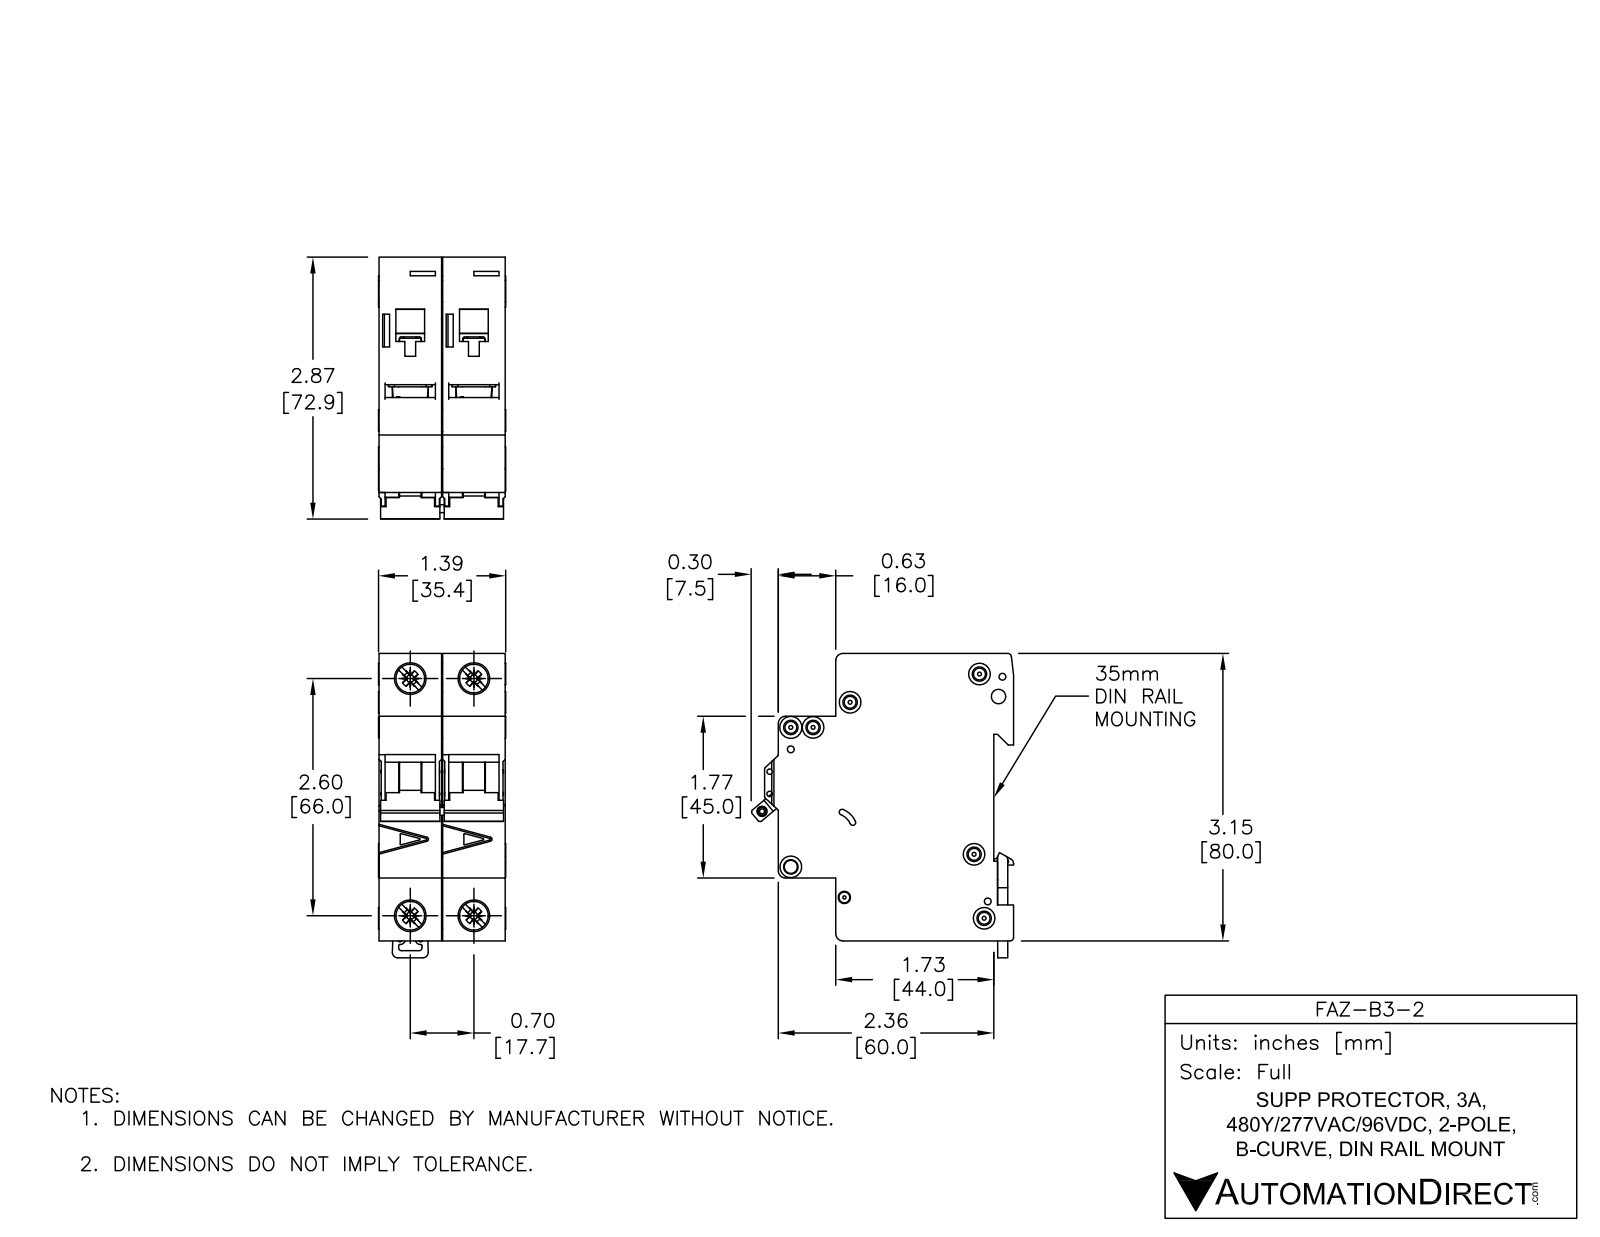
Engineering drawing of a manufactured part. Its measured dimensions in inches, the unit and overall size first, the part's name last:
Units: inches
Overall size (bounding box): 3.338 × 2.876 × 1.394
Round holes (diameter × count): ⌀0.142 ×6, ⌀0.075 ×3, ⌀0.043 ×2, ⌀0.059 ×2, ⌀0.157 ×2, ⌀0.281 ×2, ⌀0.323 ×2, ⌀0.085 ×1, ⌀0.087 ×1, ⌀0.1 ×1, ⌀0.13 ×1, ⌀0.134 ×1
Round bosses / shafts (diameter × count): ⌀0.236 ×4, ⌀0.323 ×2, ⌀0.098 ×2
Partial cylindrical surfaces — rounded edges, fillets, slot ends (radius × count): R0.01 ×49, R0.02 ×19, R0.079 ×10, R0.008 ×8, R0.039 ×8, R0.031 ×2, R0.071 ×2, R0.118 ×2
Main face-to-face distances: 0.697, 0.689, 1.386, 3.129, 0.217, 1.949, 1.732, 2.579, 2.362, 0.63
Hole centre spacings: 0.244, 0.537, 0.697, 2.598, 2.69, 0.189, 0.204, 0.221
Volume: 9.142 in³ · Surface area: 60.14 in²
Bodies: 8 solids, 1104 faces (466 planar, 396 cylindrical, 242 other)
Part name (STEP PRODUCT): FAZ-B3-2
STEP written by: SolidWorks 2014 (AUTOMOTIVE_DESIGN)
